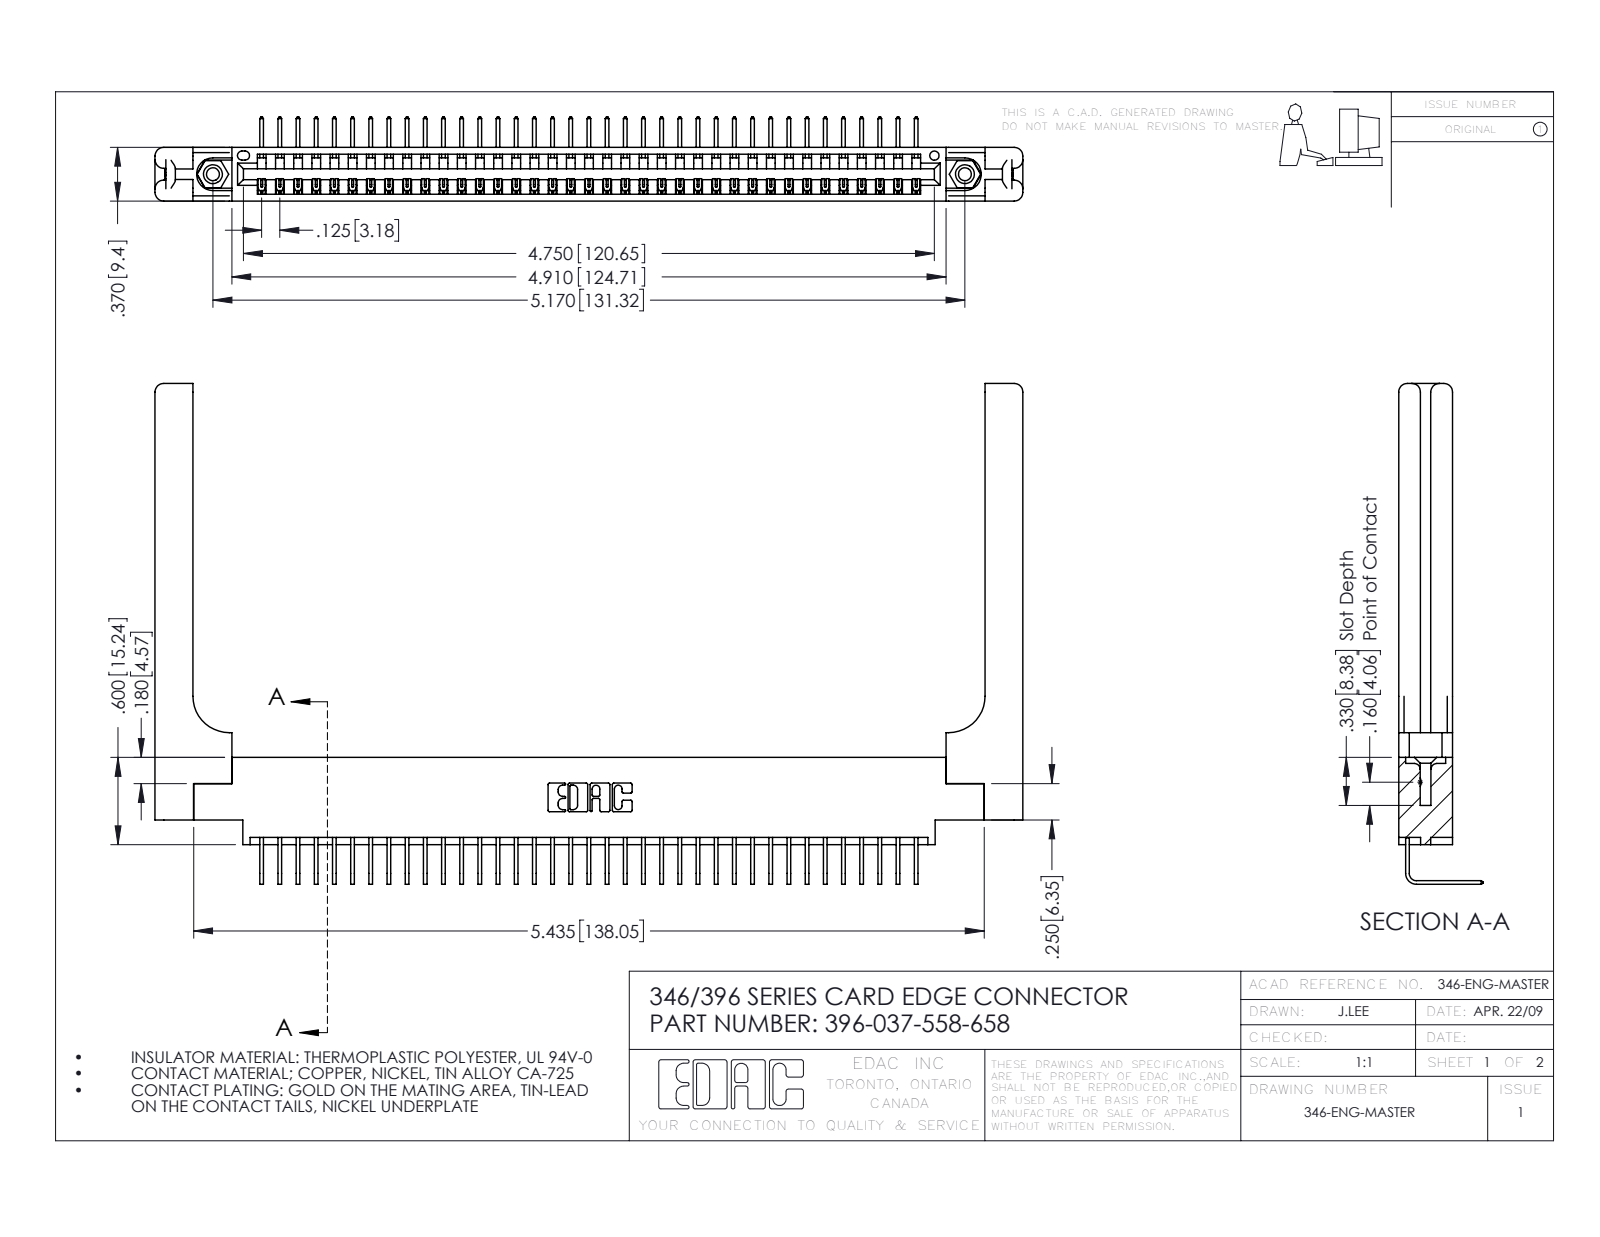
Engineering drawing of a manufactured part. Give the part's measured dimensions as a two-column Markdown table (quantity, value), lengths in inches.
| quantity | value |
| --- | --- |
| part name | 345-292-001_558 Tail - 2; 396-037-558-658; 346-220-058_345-220-058; 345-250-001_345-250-001-102 (+1 more) |
| STEP written by | SolidWorks 2016 (CONFIG_CONTROL_DESIGN) |
| units | inches |
| bodies | 42 solids, 2602 faces (1782 planar, 760 cylindrical, 60 other) |
| overall size | 5.966 × 3.443 × 0.58 |
| volume | 1.34 in³ |
| surface area | 37.29 in² |
| round holes (diameter × count) | 0.089 × 2, 0.125 × 2, 0.156 × 2, 0.064 × 1 |
| round bosses / shafts (diameter × count) | 0.155 × 2 |
| partial cylindrical surfaces (radius × count) | 0.006 × 74, 0.01 × 22, 0.06 × 16, 0.007 × 6, 0.031 × 6, 0.026 × 3, 0.03 × 2, 0.031 × 2 |
| main face-to-face distances | 0.37, 0.322, 0.048, 0.072, 0.148, 0.15, 0.025, 0.298, 0.25, 0.222 |
| hole center spacings | 0.246, 4.961, 5.17 |
